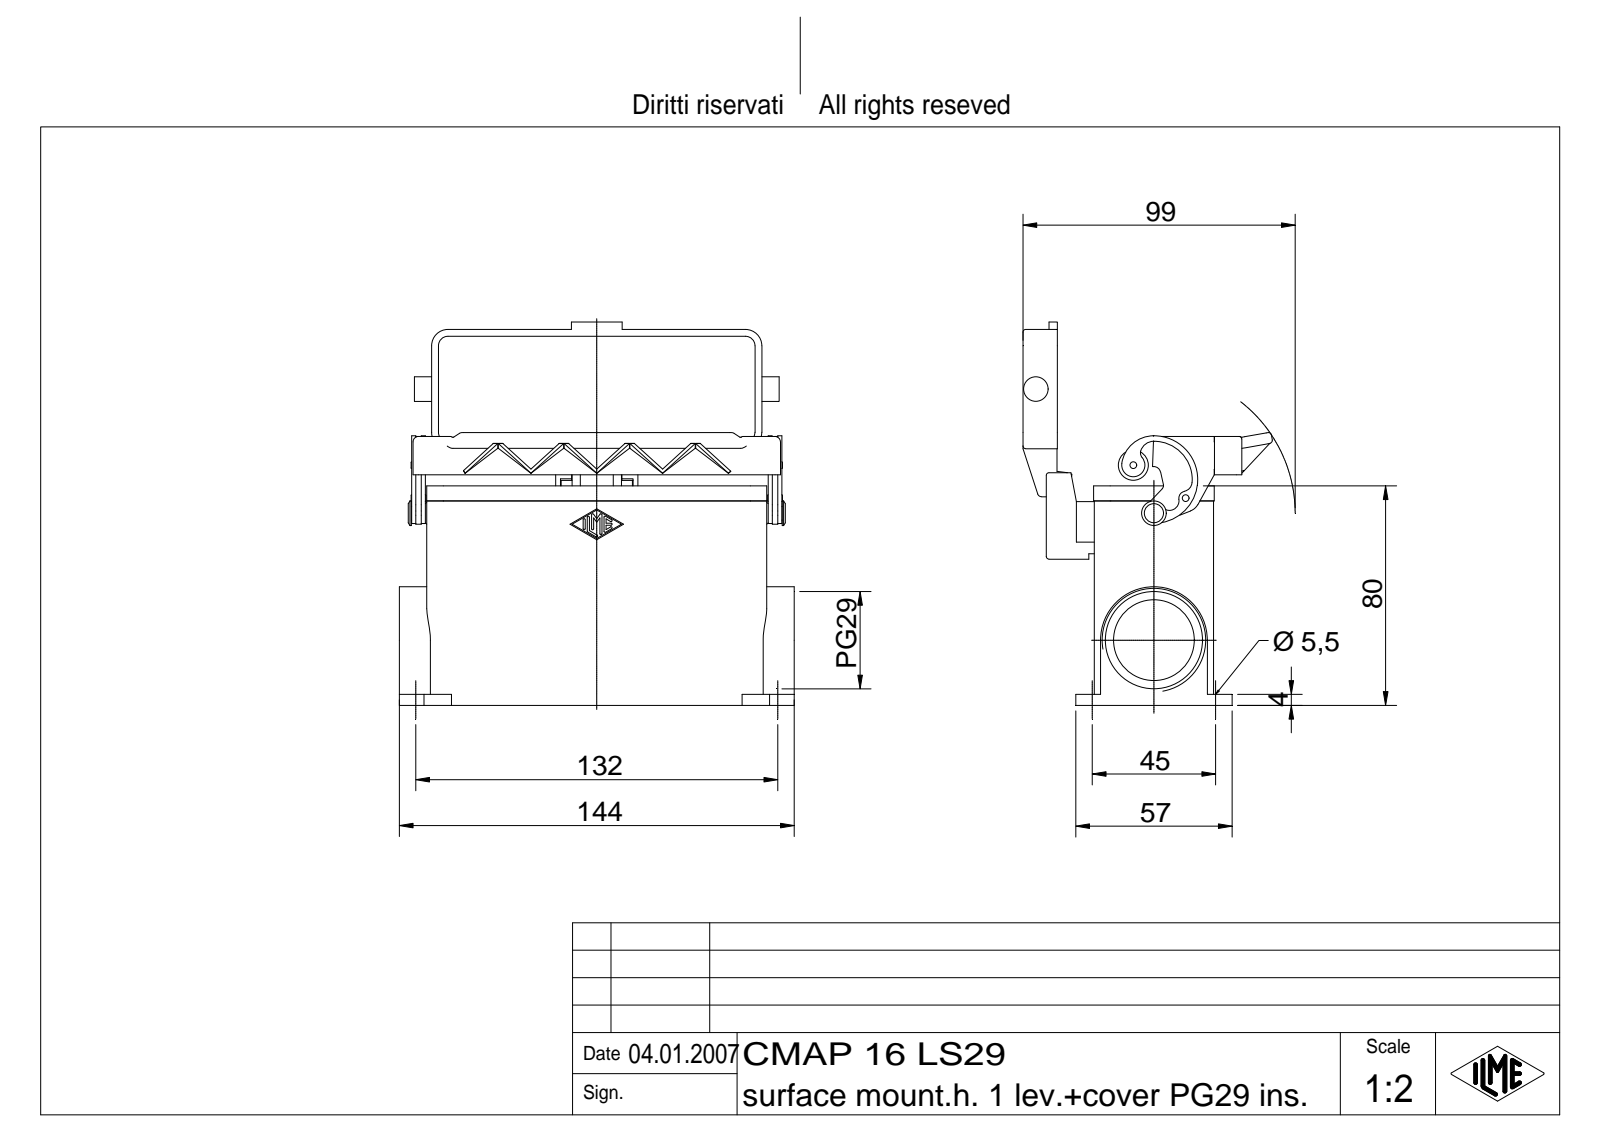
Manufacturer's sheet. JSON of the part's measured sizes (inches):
{"part_name": "CMAP 16 LS29", "step_written_by": "Autodesk Inventor 7 (AUTOMOTIVE_DESIGN)", "units": "inches", "bodies": {"solids": 6, "faces": 626, "planar": 282, "cylindrical": 180, "other": 164}, "overall_size": [5.669, 5.5, 3.581], "volume_in3": 11.43, "surface_area_in2": 166, "round_holes": [[0.217, 4], [0.079, 1], [0.157, 1], [1.161, 1], [1.397, 1]], "round_bosses_or_shafts": [[0.354, 2], [0.197, 2], [0.433, 1], [0.276, 1], [0.157, 1], [0.118, 1], [0.098, 1]], "partial_cylinders_radius": [[0.039, 18], [0.015, 14], [0.079, 12], [0.236, 12], [0.059, 6], [0.138, 6], [0.118, 4], [0.02, 3]], "face_to_face_distances": [0.118, 1.594, 1.713, 0.157, 1.476, 1.024, 2.618, 2.736, 1.142, 0.138], "hole_center_spacings": [1.772, 5.197, 5.491, 2.088]}
